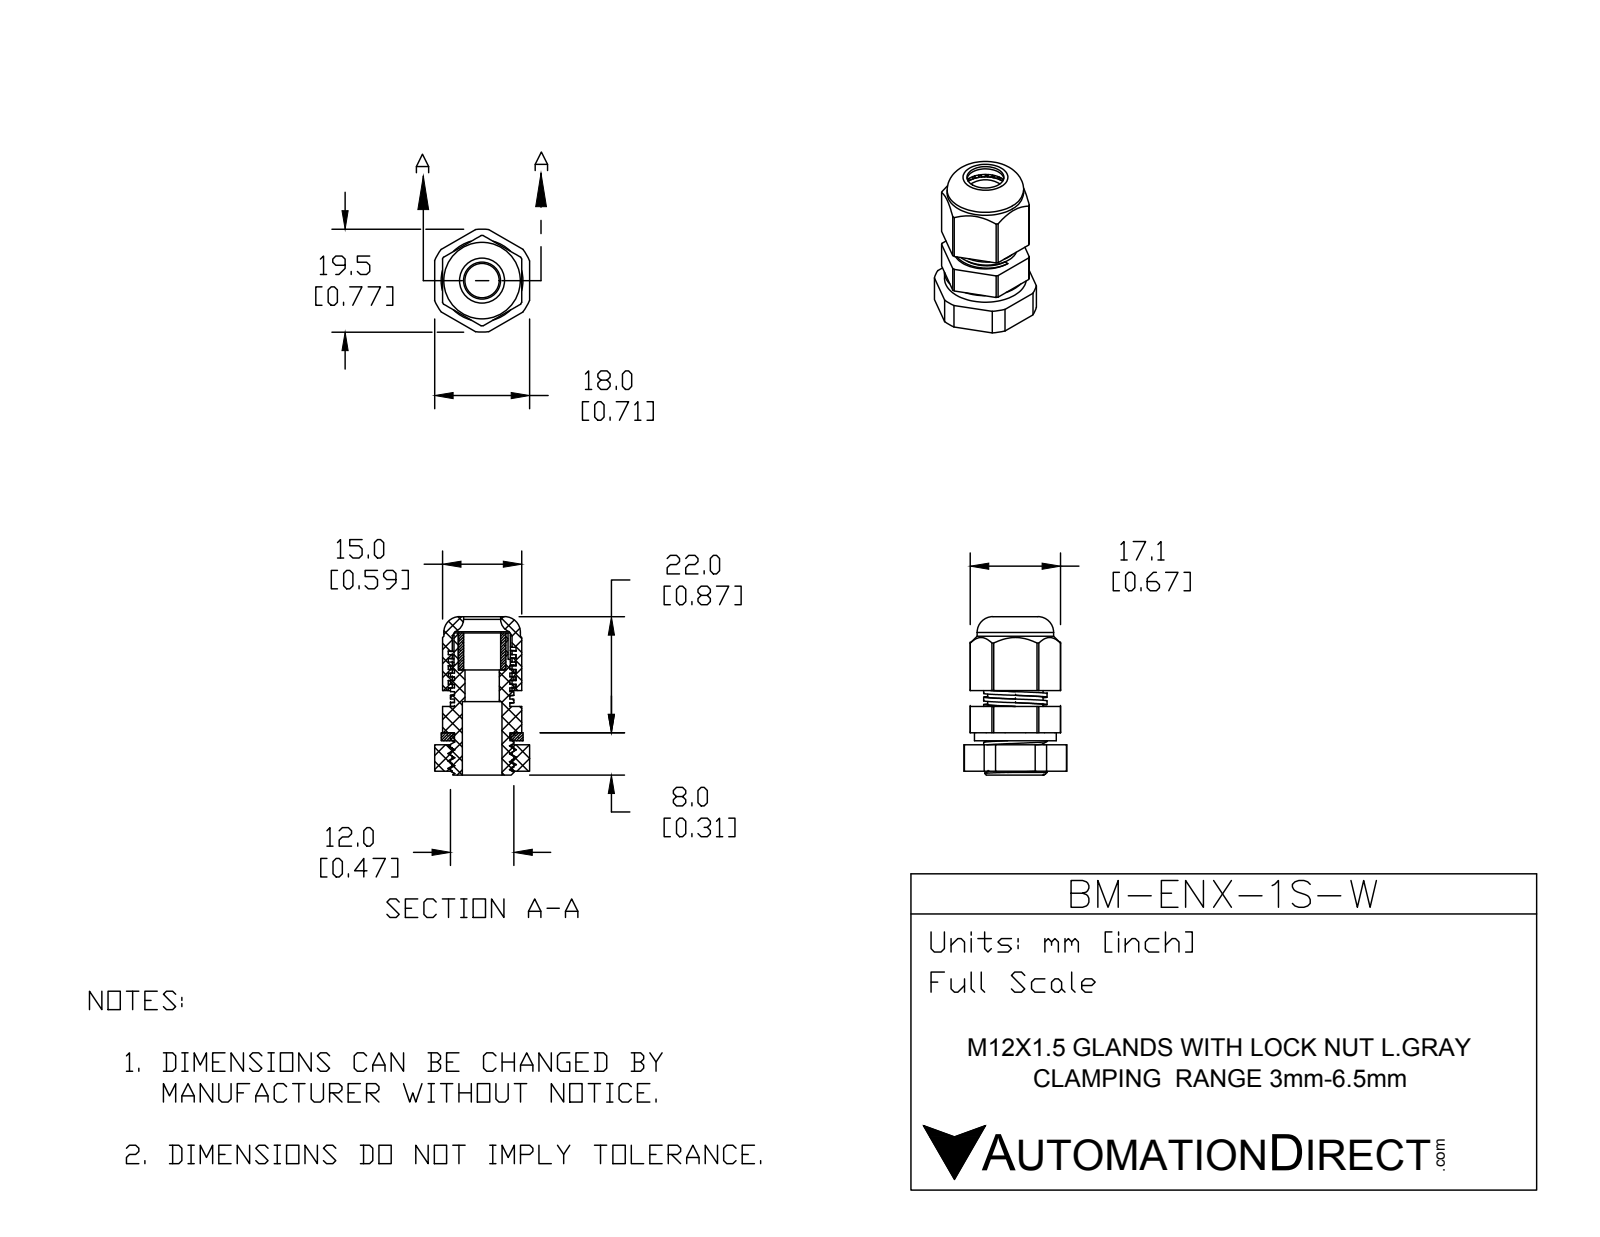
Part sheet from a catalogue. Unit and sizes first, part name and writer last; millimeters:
Units: millimetres
Overall size (bounding box): 30 × 19.5 × 18
Round holes (diameter × count): ⌀6.5 ×1, ⌀7 ×1, ⌀7.5 ×1, ⌀9 ×1, ⌀10.5 ×1, ⌀11.33 ×1
Round bosses / shafts (diameter × count): ⌀15.5 ×1, ⌀14.5 ×1, ⌀12 ×1, ⌀10.7 ×1
Partial cylindrical surfaces — rounded edges, fillets, slot ends (radius × count): R8.55 ×1, R9.75 ×1
Main face-to-face distances: 15, 1.5, 5, 7.27, 16.5, 2.27, 6.5, 8, 18, 0.5
Volume: 4 119 mm³ · Surface area: 5 943 mm²
Bodies: 5 solids, 244 faces (134 planar, 88 cylindrical, 22 other)
Part name (STEP PRODUCT): BM-ENX-1S-W
STEP written by: SolidWorks 2015 (CONFIG_CONTROL_DESIGN)
